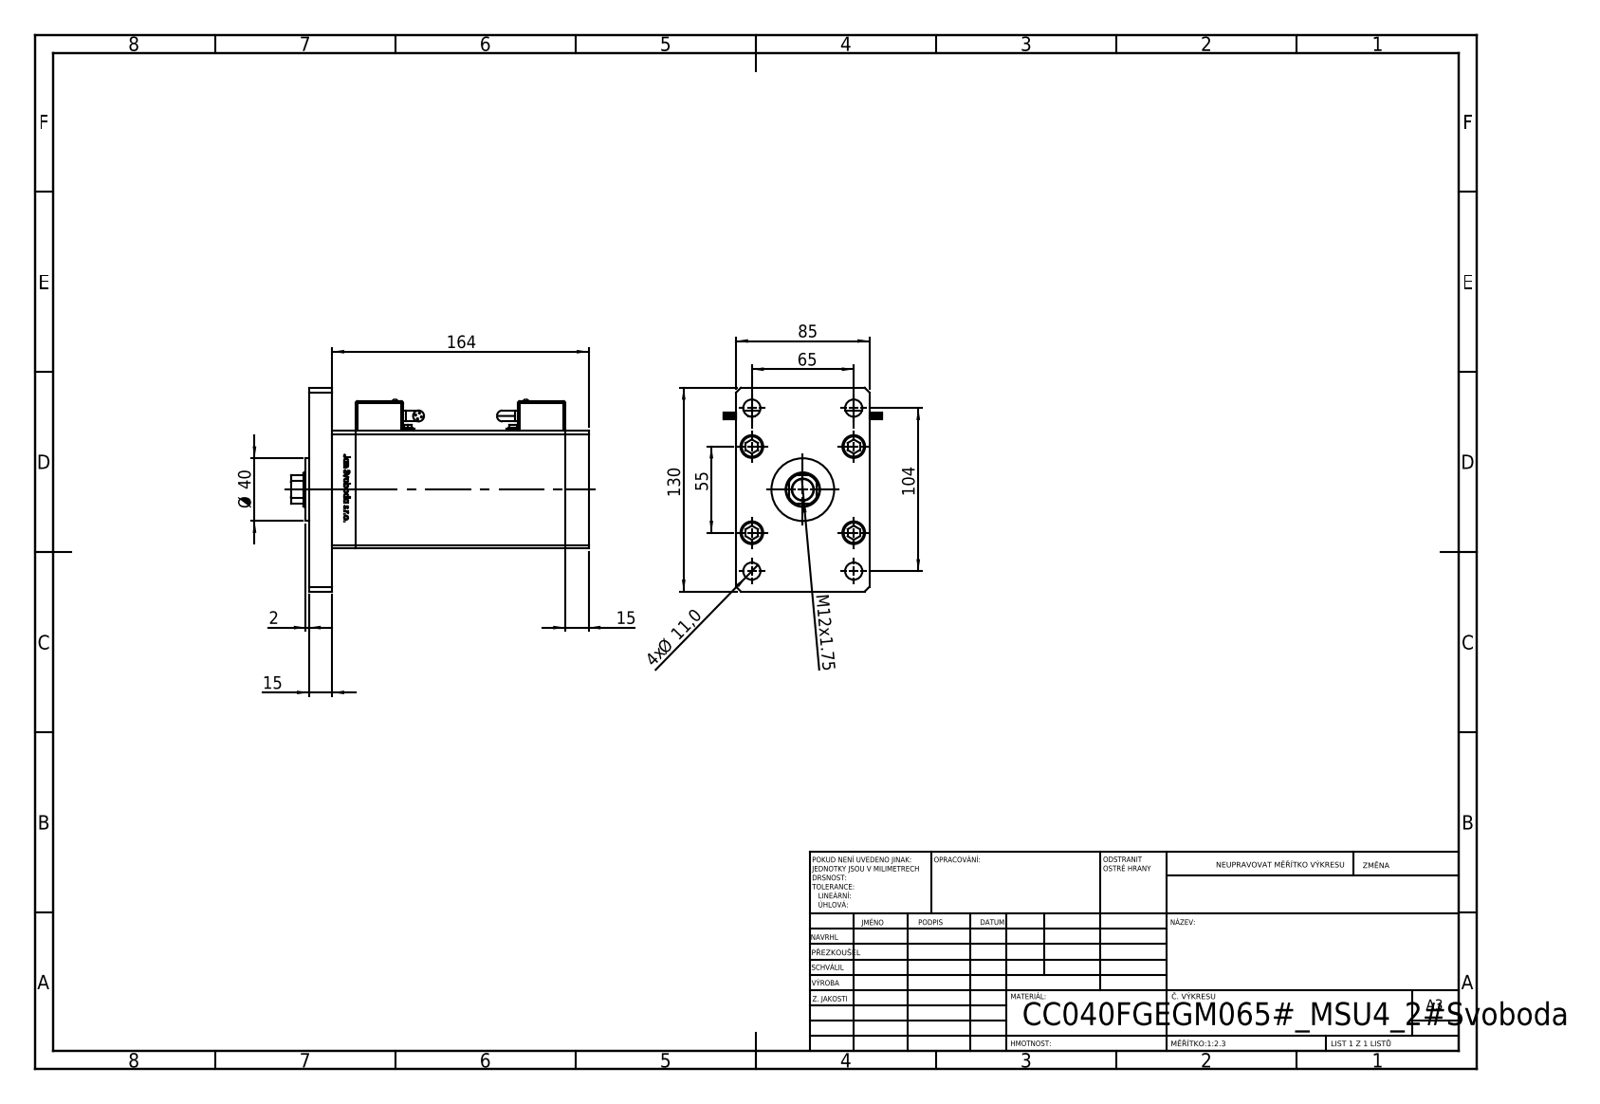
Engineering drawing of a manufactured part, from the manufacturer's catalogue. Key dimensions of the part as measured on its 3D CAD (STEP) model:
Part name (STEP PRODUCT): V220C BACK_F; V220C_VC_F; V220C_FRONT_F; ALLEN BOLT (+3 more)
STEP written by: SolidWorks 2019 (CONFIG_CONTROL_DESIGN)
Units: millimetres
Bodies: 21 solids, 1514 faces (595 planar, 277 cylindrical, 642 other)
Overall size (bounding box): 190 × 130 × 101.6
Volume: 1 123 000 mm³ · Surface area: 202 200 mm²
Round holes (diameter × count): ⌀11 ×9, ⌀15.5 ×5, ⌀10 ×4, ⌀14.5 ×4, ⌀2 ×2, ⌀3.6 ×2, ⌀5 ×2, ⌀7 ×2, ⌀13.16 ×2, ⌀13.5 ×1, ⌀22 ×1, ⌀23.5 ×1
Round bosses / shafts (diameter × count): ⌀8 ×9, ⌀0.85 ×8, ⌀14.5 ×5, ⌀7 ×4, ⌀6 ×2, ⌀3.5 ×2, ⌀2.5 ×2, ⌀40 ×1
Partial cylindrical surfaces — rounded edges, fillets, slot ends (radius × count): R1 ×24, R4 ×4, R0.93 ×2, R10.5 ×1
Main face-to-face distances: 15, 148.5, 163.5, 85, 30, 133.5, 75, 178.5, 10.5, 27.5
Hole centre spacings: 28, 24.5, 42.57, 61.32, 65, 69.46, 79.5, 102.69
